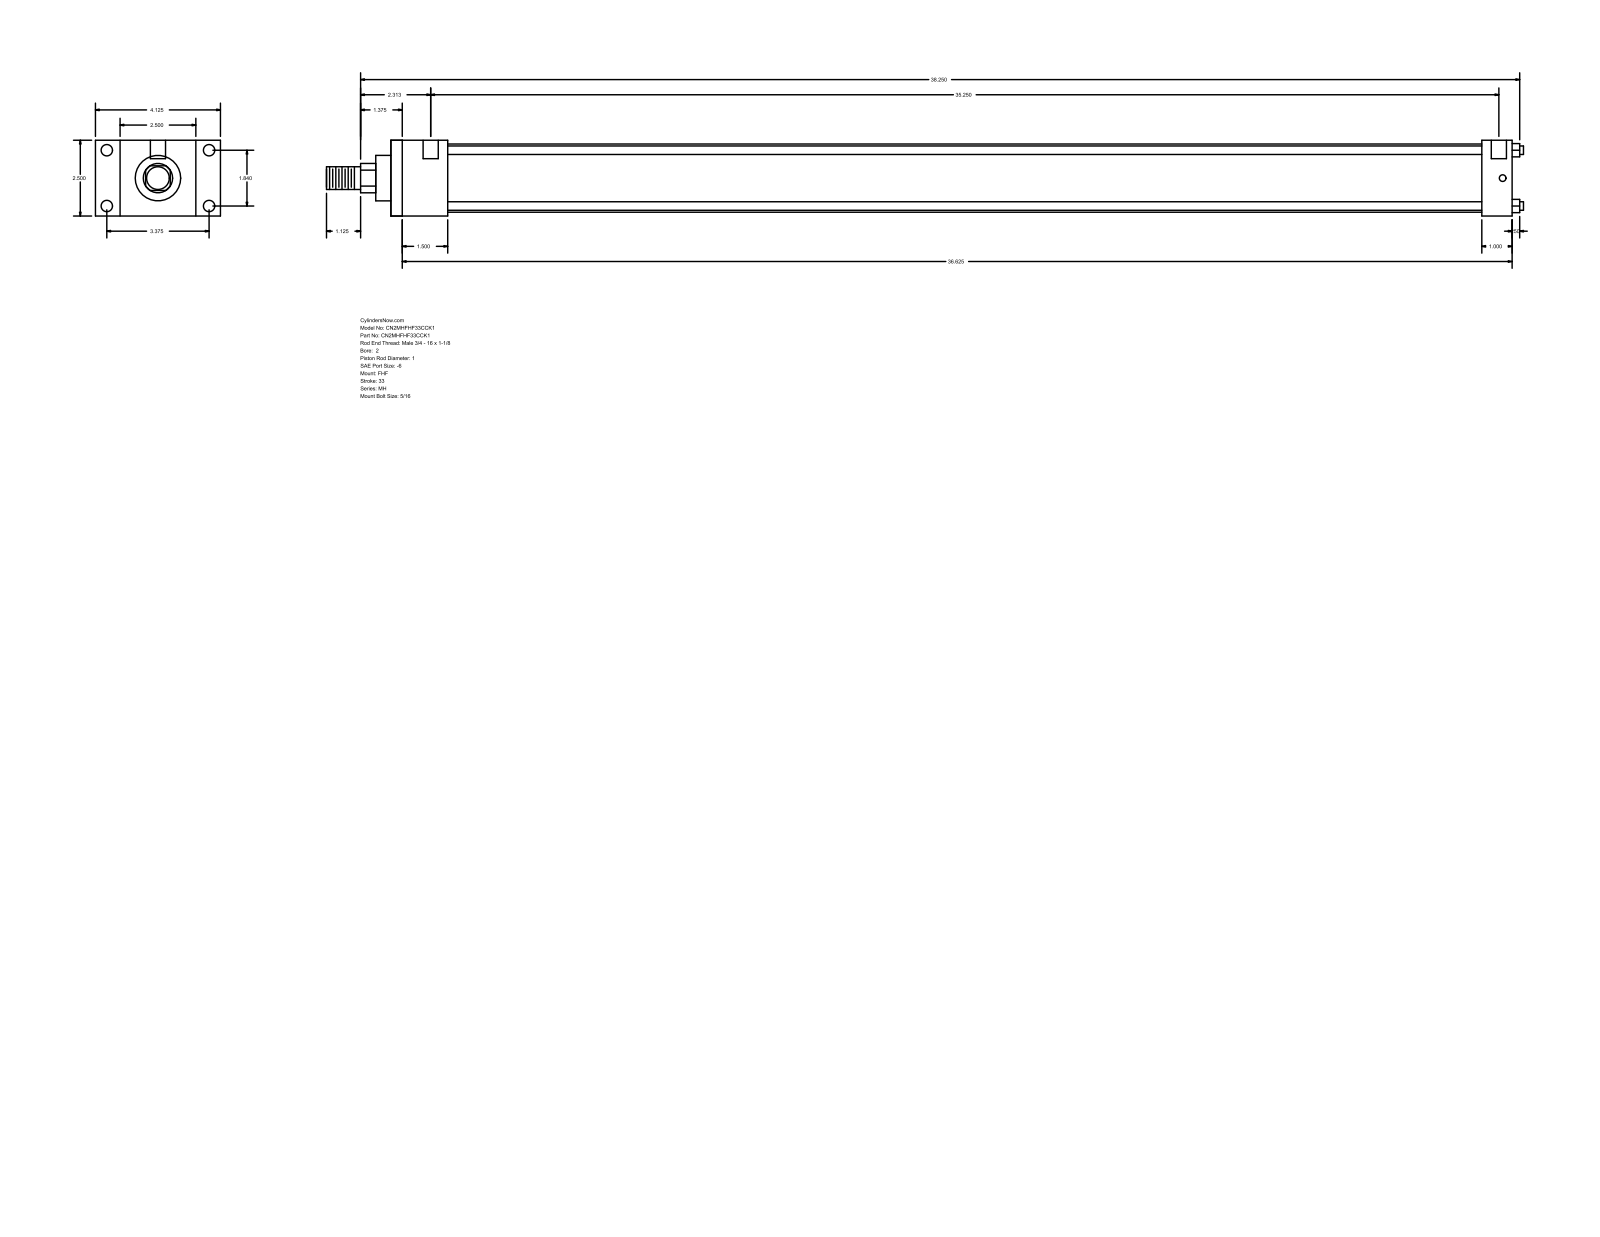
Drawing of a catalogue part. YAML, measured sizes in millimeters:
part_name: "MH_FHF__0200_1"
step_written_by: "GSSL Pune (CONFIG_CONTROL_DESIGN)"
units: millimeters
bodies: {solids: 0, faces: 88, planar: 60, cylindrical: 28, other: 0}
overall_size: [1003.3, 104.78, 63.5]
round_holes:
  - {diameter: 5.56, count: 4}
  - {diameter: 9.53, count: 4}
  - {diameter: 12.7, count: 2}
round_bosses_or_shafts:
  - {diameter: 7.14, count: 4}
  - {diameter: 57.15, count: 1}
  - {diameter: 38.1, count: 1}
  - {diameter: 25.4, count: 1}
  - {diameter: 19.05, count: 1}
partial_cylinders:
  - {radius: 12.29, count: 1}
face_to_face_distances: [63.5, 939.8, 47.63, 892.17, 20.64, 84.14, 104.78, 25.4, 914.4, 866.77]
hole_center_spacings: [46.74, 85.72, 97.63, 903.28, 3.17, 4.76, 895.35, 898.52]
